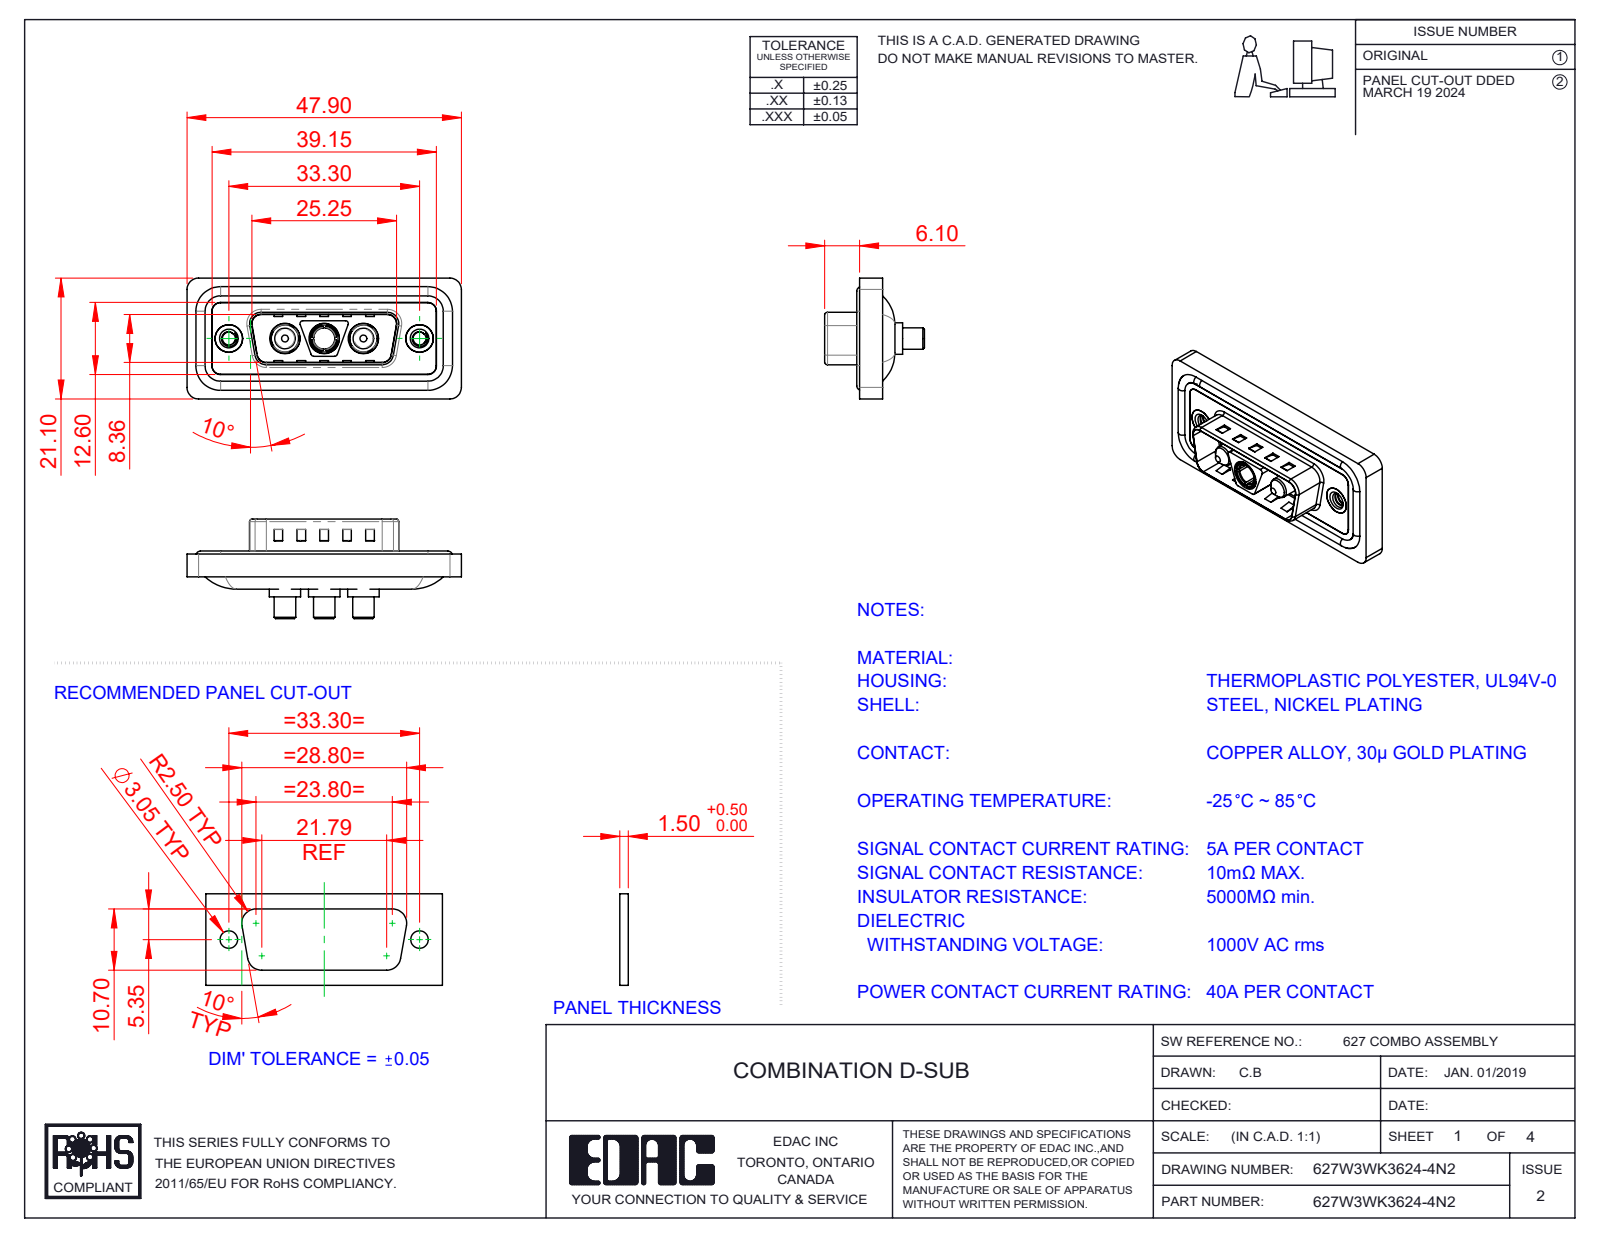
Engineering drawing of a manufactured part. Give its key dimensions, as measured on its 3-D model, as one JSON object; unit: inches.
{"part_name": "627Combo Threaded Rivet_2; 627Combo Waterproof Housing_15 Contacts; 627Combo Shell Rear_15 Contacts; Power Pin_40A S (+4 more)", "step_written_by": "SolidWorks 2023 (CONFIG_CONTROL_DESIGN)", "units": "inches", "bodies": {"solids": 13, "faces": 609, "planar": 231, "cylindrical": 250, "other": 128}, "overall_size": [1.886, 0.831, 0.685], "volume_in3": 0.35, "surface_area_in2": 14.2, "round_holes": [[0.191, 3], [0.209, 3], [0.089, 2], [0.157, 2], [0.189, 2], [0.197, 2], [0.146, 1]], "round_bosses_or_shafts": [[0.063, 4], [0.217, 3], [0.205, 3], [0.187, 3], [0.148, 3], [0.193, 2], [0.142, 2], [0.195, 1]], "partial_cylinders_radius": [[0.059, 26], [0.079, 20], [0.02, 12], [0.063, 8], [0.01, 4], [0.024, 4], [0.026, 4], [0.035, 4]], "face_to_face_distances": [0.016, 0.043, 0.02, 0.059, 0.063, 0.122, 0.114, 0.157, 0.032, 0.377], "hole_center_spacings": [0.27, 0.386, 0.656, 0.925, 0.539, 1.311]}
